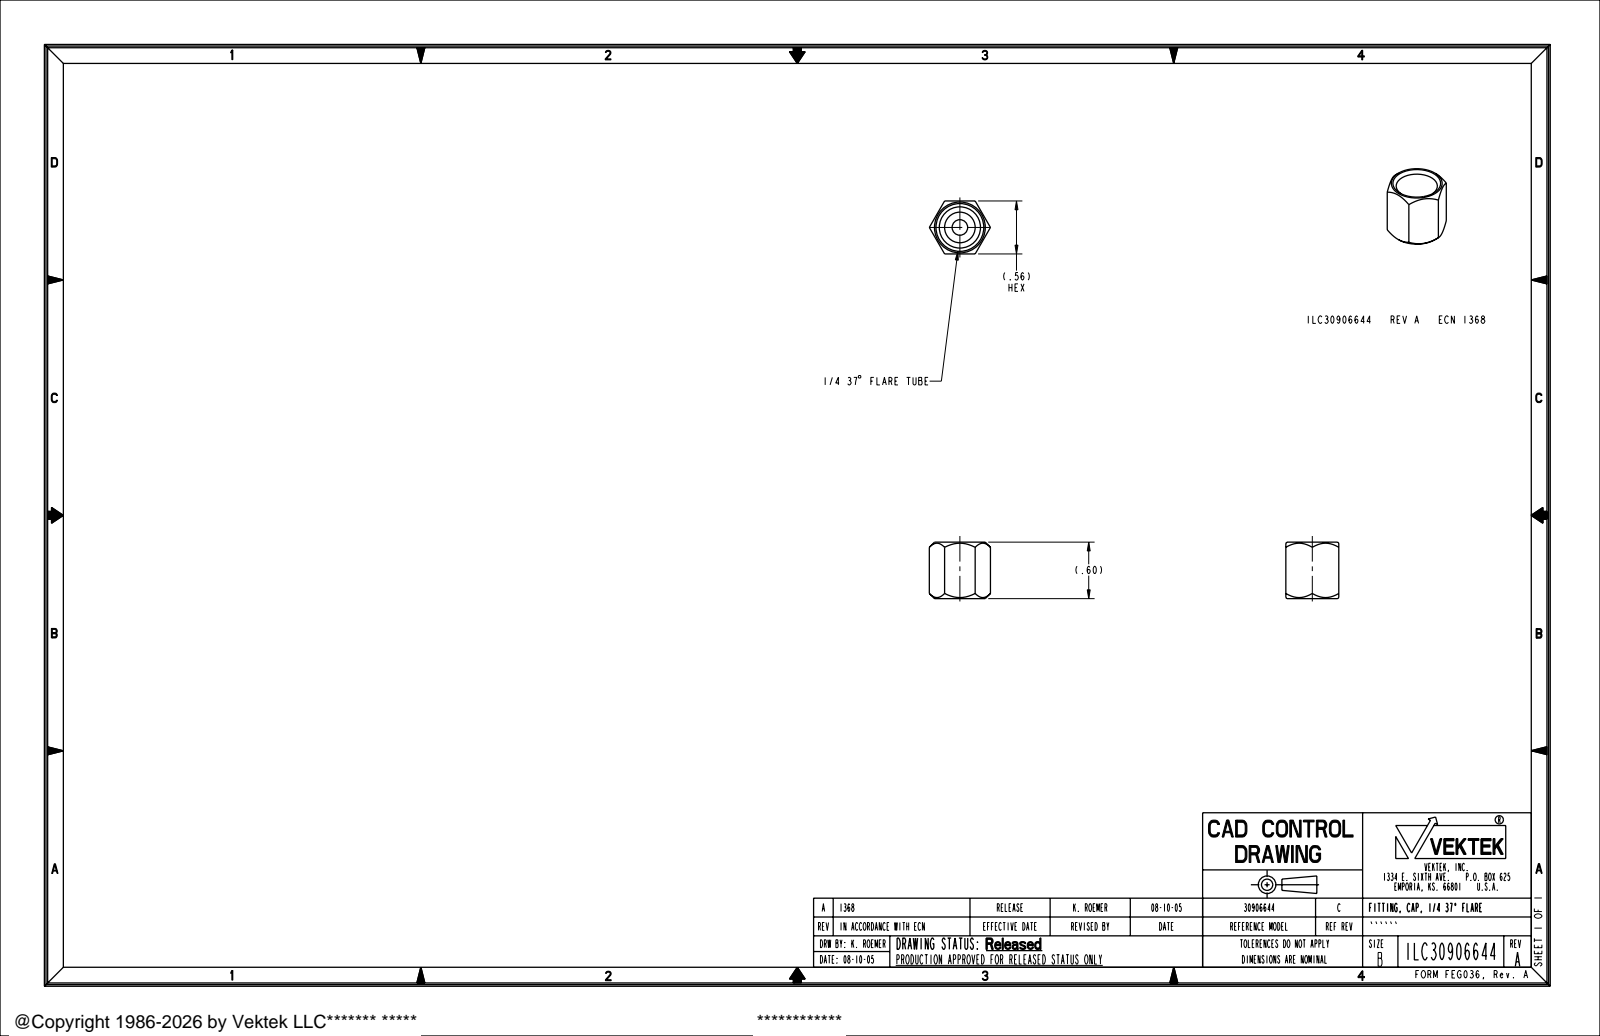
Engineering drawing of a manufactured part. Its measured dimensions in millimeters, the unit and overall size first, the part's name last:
Units: millimetres
Overall size (bounding box): 16.5 × 15.2 × 14.3
Round holes (diameter × count): ⌀4.2 ×1, ⌀11.1 ×1
Main face-to-face distances: 14.3, 6.6, 15.2, 8.6, 1.8, 4.8, 13.5
Volume: 1 720 mm³ · Surface area: 1 404 mm²
Bodies: 1 solid, 22 faces (10 planar, 4 cylindrical, 8 other)
Part name (STEP PRODUCT): ILC30906644
STEP written by: PRO/ENGINEER BY PARAMETRIC TECHNOLOGY CORPORATION, 2004290 (AUTOMOTIVE_DESIGN_CC2)
